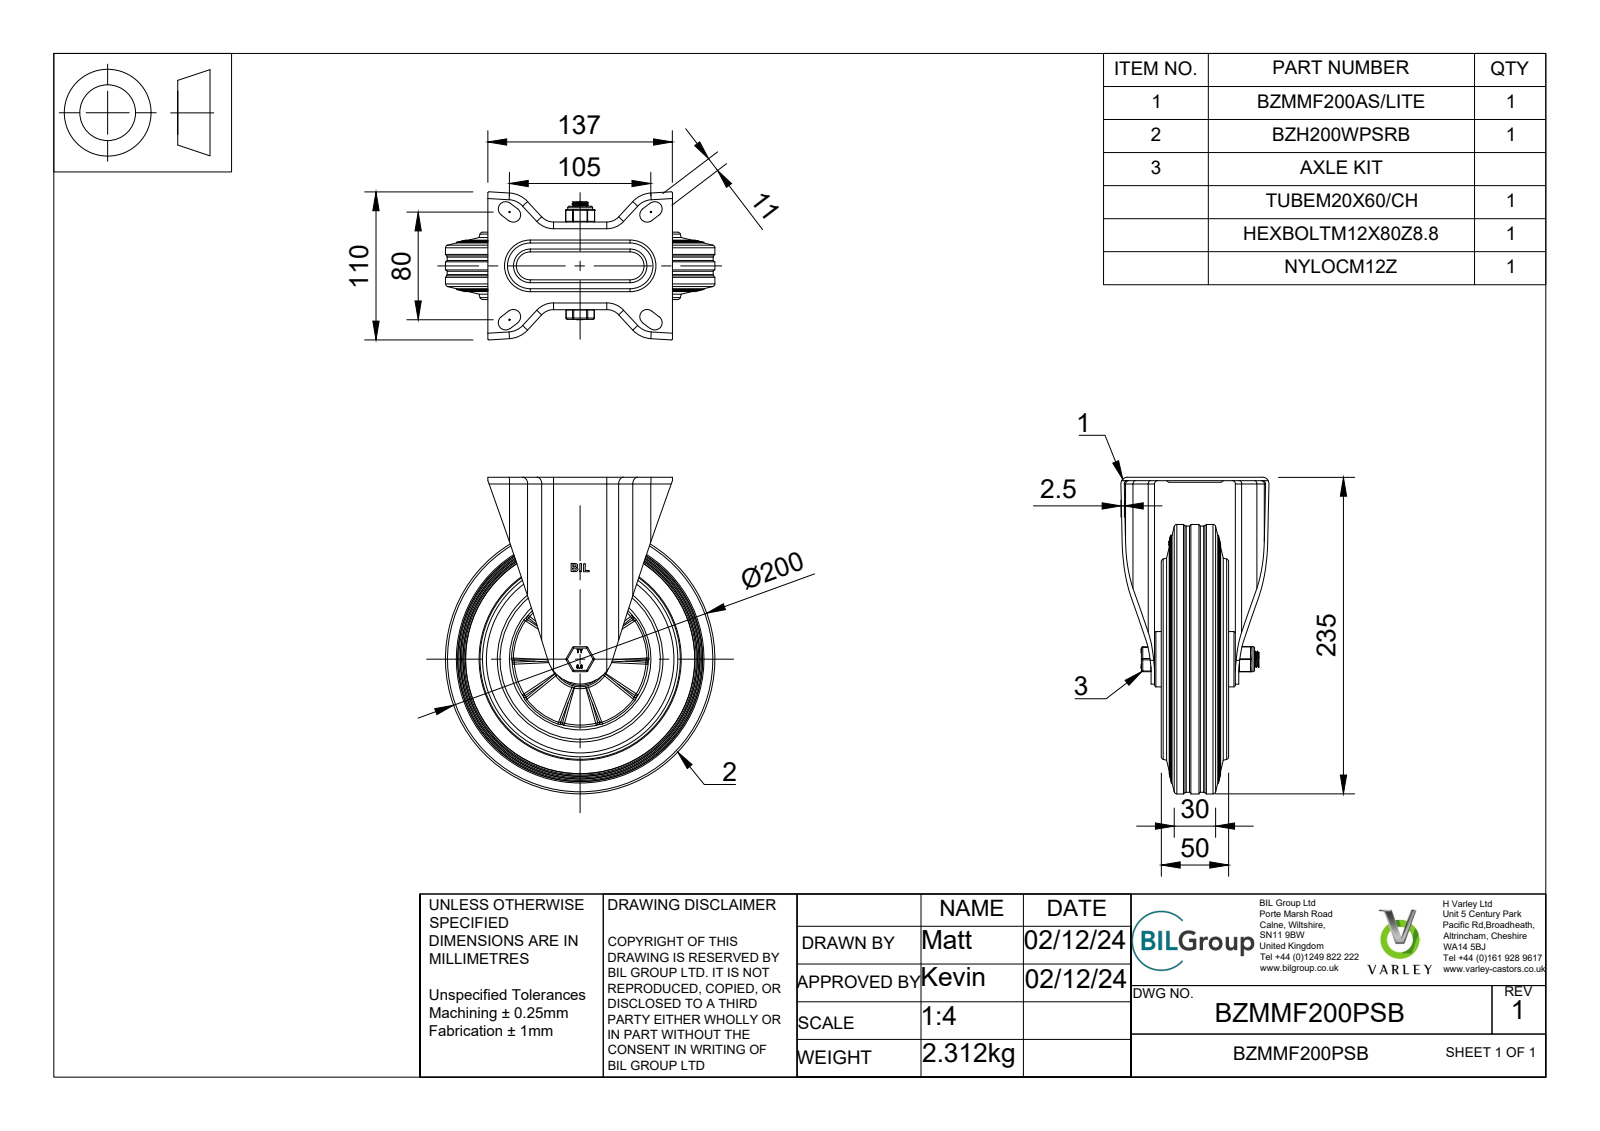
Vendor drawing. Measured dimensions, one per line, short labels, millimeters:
name: BZMMF200PSB v4; BZMMF200AS/LITE v4; ZINC PLATED, PRESSED STEELM BRACKET; BZH200WPSRB v1 (+7 more)
written by: Autodesk Translation Framework v13.20.0.188 (AP242_MANAGED_MODEL_BASED_3D_ENGINEERING_MIM_LF)
unit: mm
bodies: 17 solids, 849 faces (225 planar, 190 cylindrical, 434 other)
size: 235 × 200 × 109.89
volume: 1 164 000 mm³; area: 287 294 mm²
holes: 1× ⌀12, 1× ⌀12.25, 1× ⌀12.5, 1× ⌀14, 1× ⌀20, 1× ⌀35, 1× ⌀101, 1× ⌀118
bosses: 8× ⌀7.5, 1× ⌀200, 1× ⌀197.5, 1× ⌀123, 1× ⌀41, 1× ⌀34.9, 1× ⌀34, 1× ⌀19.9
rounds: 18× R0.5, 18× R2.5, 12× R1, 10× R5, 8× R5.5, 4× R12, 4× R14.5, 4× R17.5
face distances: 2.5, 62.5, 9, 53.5, 60, 6.5, 5, 51.5, 48.5, 11.5
